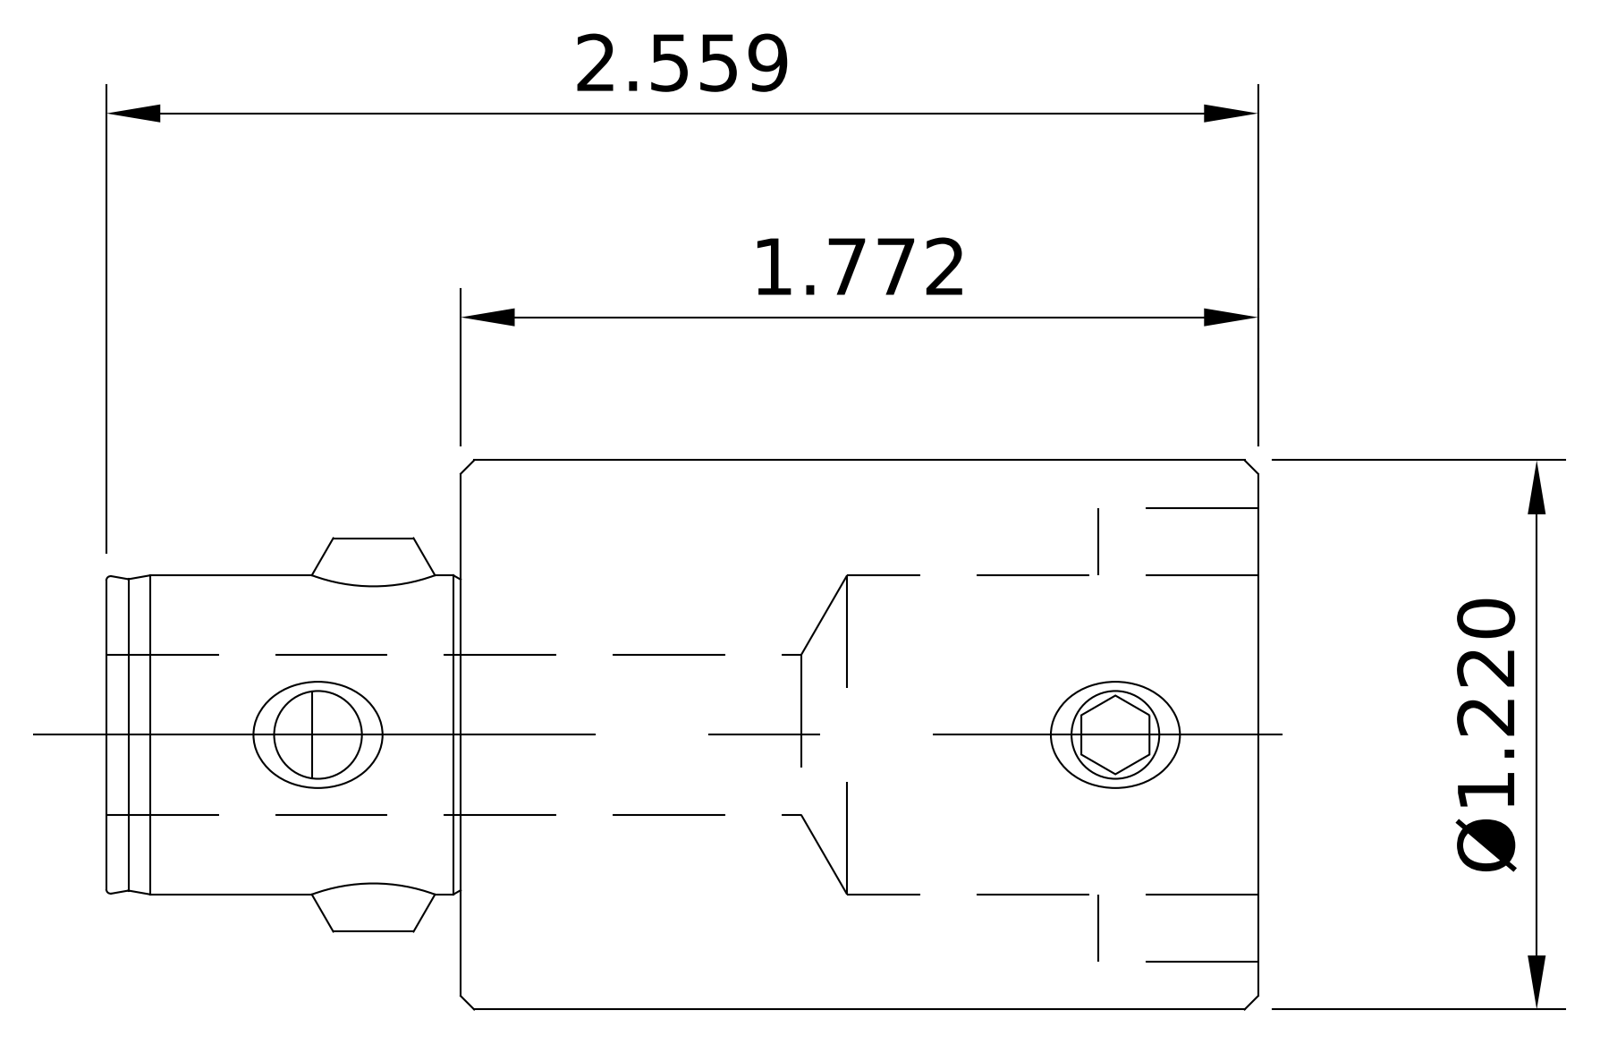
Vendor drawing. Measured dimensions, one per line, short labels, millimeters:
name: 10.690.43X_10.690.433; 11.331.331; 10.691.50X_10.691.503; 691-50XRing_10.691.503Ring
written by: SolidWorks 2018 (CONFIG_CONTROL_DESIGN)
unit: mm
bodies: 4 solids, 122 faces (35 planar, 40 cylindrical, 47 other)
size: 65 × 31 × 31
volume: 30 261 mm³; area: 10 340 mm²
holes: 2× ⌀5, 1× ⌀4.5, 1× ⌀6.2, 1× ⌀7, 1× ⌀9, 1× ⌀18, 1× ⌀18.5
bosses: 1× ⌀31, 1× ⌀6.9, 1× ⌀6, 1× ⌀4
rounds: 2× R2.75, 1× R9
face distances: 45, 20, 65, 15.54, 56.1, 36.1, 8.9, 1, 3.1, 4.1
hole spacings: 44.7
